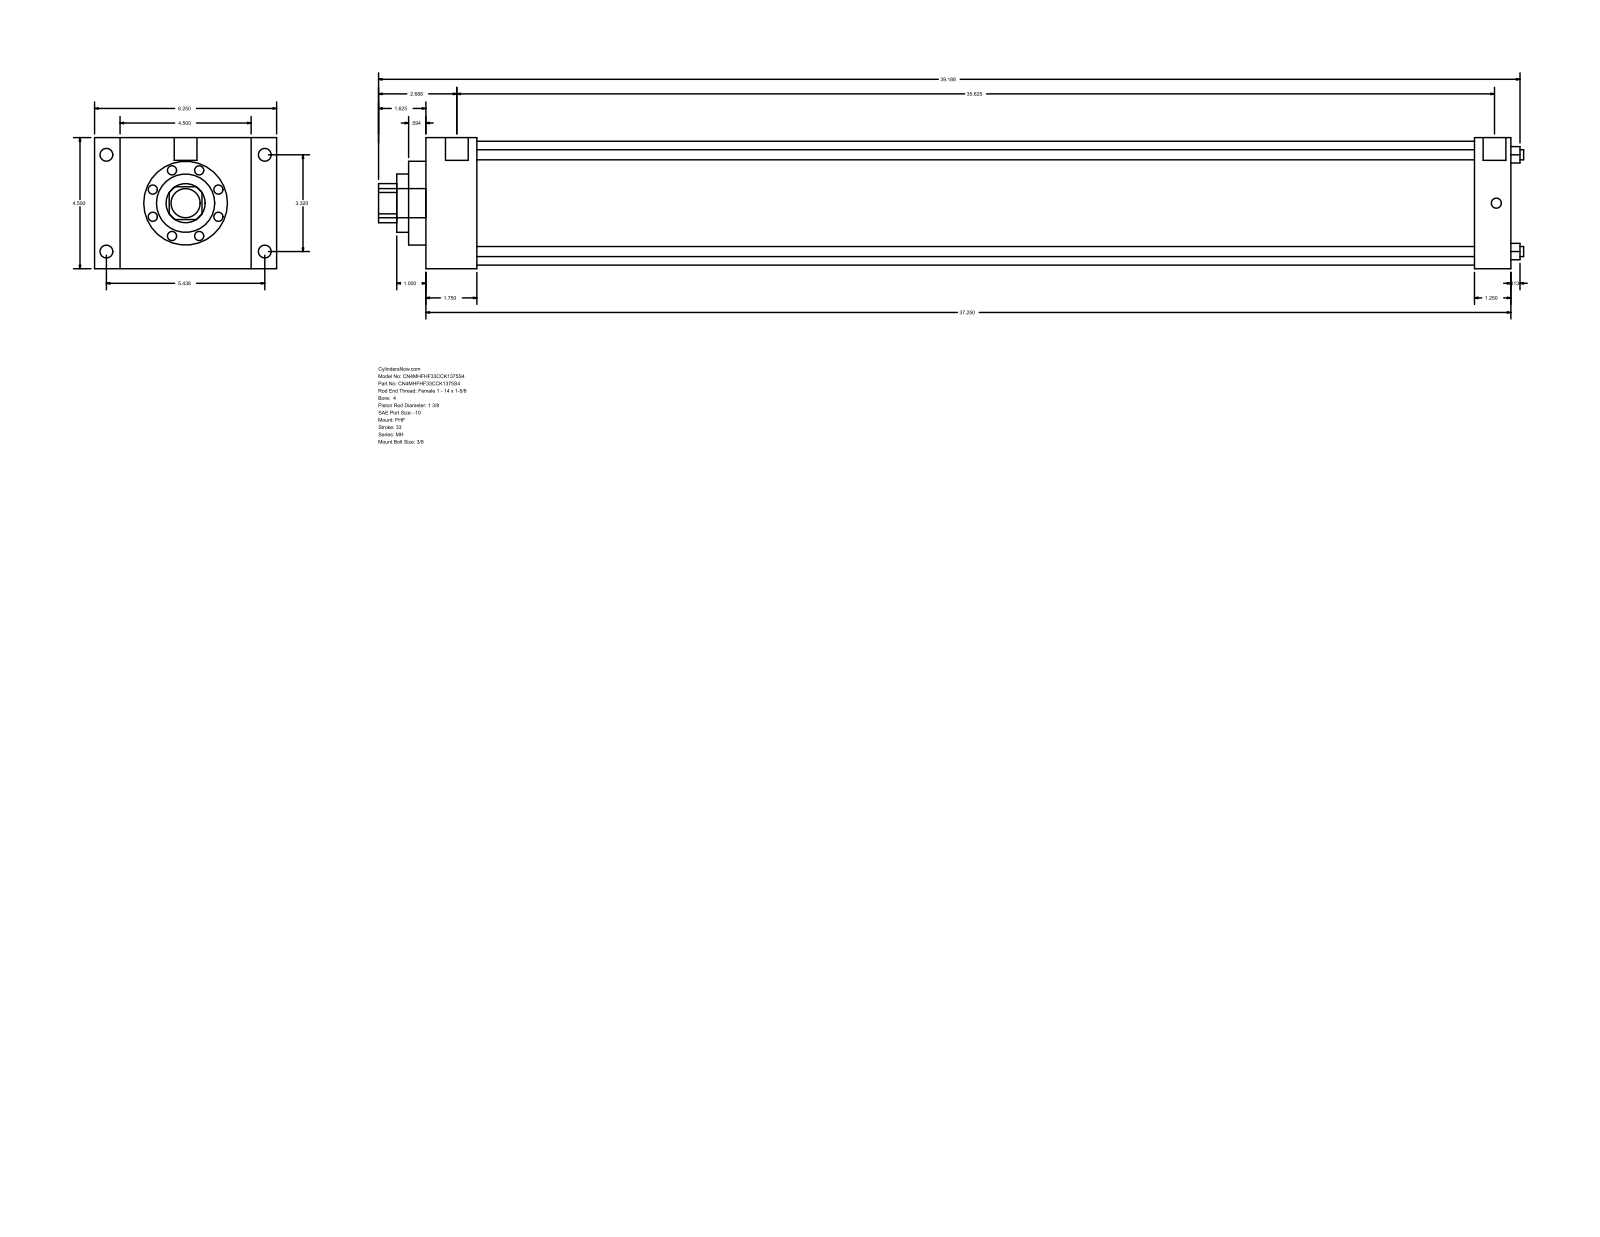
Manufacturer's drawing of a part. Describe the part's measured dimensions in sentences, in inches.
The part is named "MH_FHF__0400_1.375". Its 3-D file was written by "GSSL Pune (CONFIG_CONTROL_DESIGN)". It is 0 solids with 90 faces: 61 planar, 29 cylindrical and 0 other. Overall it measures 39.313 by 6.25 by 4.5 inches. Round holes: 4 of diameter 0.345, 1 of diameter 1.375, 1 of diameter 2, 1 of diameter 2.875, 1 of diameter 4.25. Round bosses or shafts: 4 of diameter 0.438, 4 of diameter 0.344, 2 of diameter 0.781, 1 of diameter 1. Partial cylindrical surfaces (rounded edges, fillets, slot ends): 1 of radius 0.672. The main face-to-face distances are 4.5, 37.25, 1.75, 35.5, 0.875, 5.375, 6.25, 36, 34.25, 1.25. The hole center spacings are 2.347, 3.32, 4.695.
